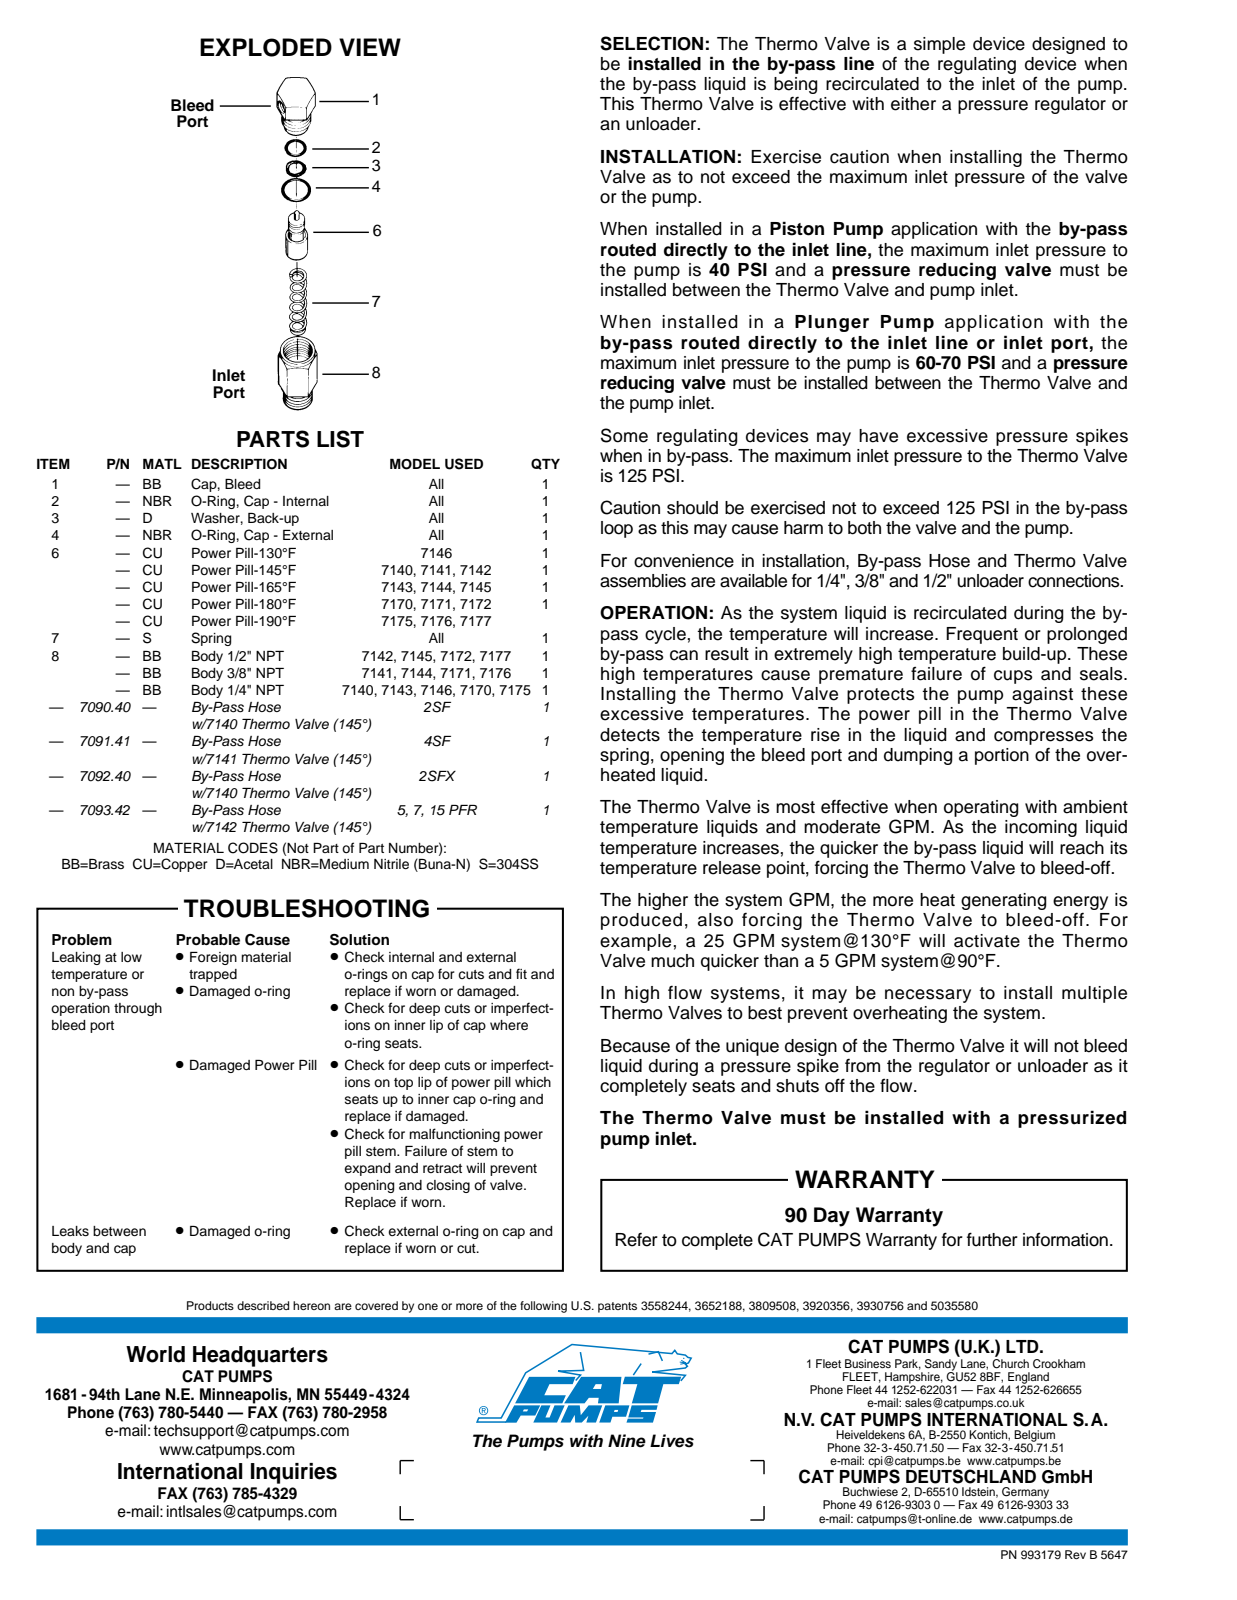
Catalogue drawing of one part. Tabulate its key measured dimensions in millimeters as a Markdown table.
| quantity | value |
| --- | --- |
| part name | 7140 |
| STEP written by | SolidWorks 2012 (AUTOMOTIVE_DESIGN) |
| units | millimeters |
| bodies | 0 solids, 40 faces (18 planar, 6 cylindrical, 16 other) |
| overall size | 79.38 × 25.66 × 22.23 |
| round holes (diameter × count) | 8.43 × 1 |
| round bosses / shafts (diameter × count) | 21.97 × 1, 21.84 × 1 |
| main face-to-face distances | 21.98, 22.1, 22.22, 16.76, 62.61, 79.37, 15.3, 15.18, 6.8, 6.92 |
